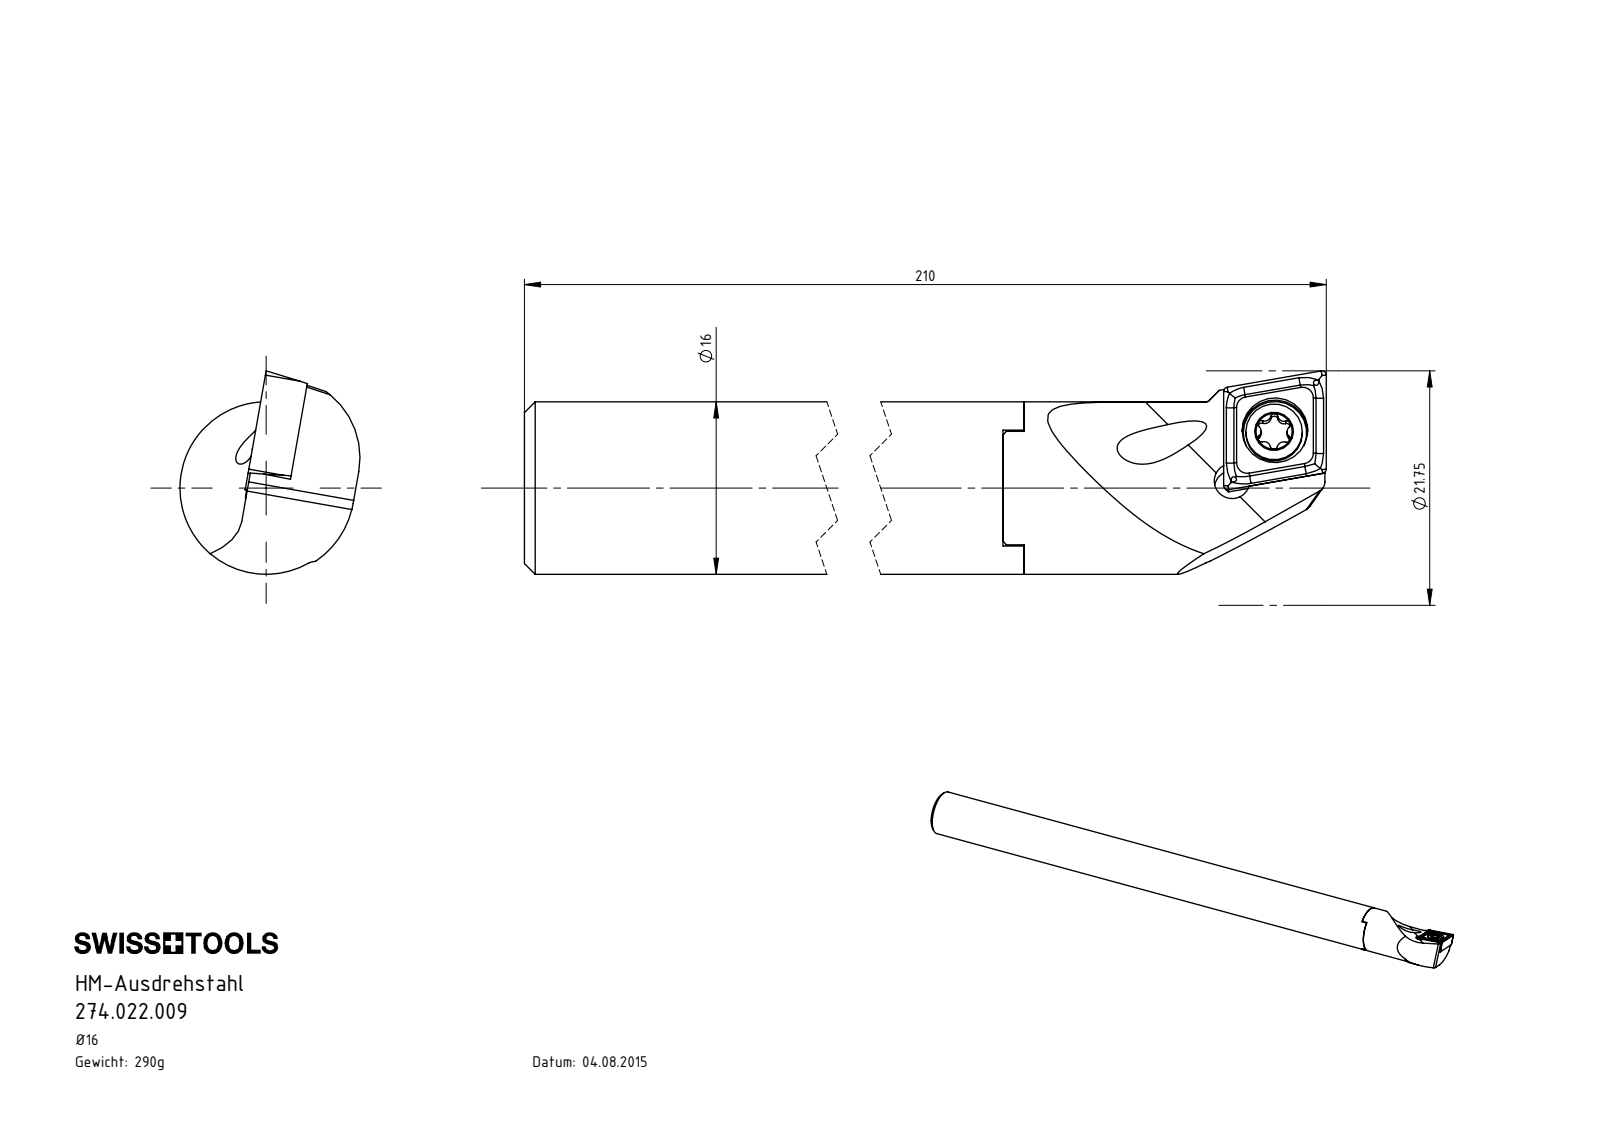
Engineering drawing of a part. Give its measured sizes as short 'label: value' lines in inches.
name: CCMT09T304; HM2-U16.001.182_A; WCB-ER2.001.009_A; HM2-BG1.001.030_B (+2 more)
written by: SolidWorks 2012 (CONFIG_CONTROL_DESIGN)
unit: in
bodies: 4 solids, 142 faces (44 planar, 40 cylindrical, 58 other)
size: 8.268 × 0.743 × 0.678
volume: 2.253 in³; area: 22.78 in²
holes: 2× ⌀0.13, 1× ⌀0.118, 1× ⌀0.173, 1× ⌀0.197, 1× ⌀0.24
bosses: 1× ⌀0.63, 1× ⌀0.207, 1× ⌀0.157
rounds: 6× R0.013, 6× R0.023, 1× R0.323, 1× R0.394
face distances: 7.163, 7.087, 0.077, 0.15, 0.241, 0.391, 0.471, 0.397, 0.156, 0.467
hole spacings: 0.239, 0.244
